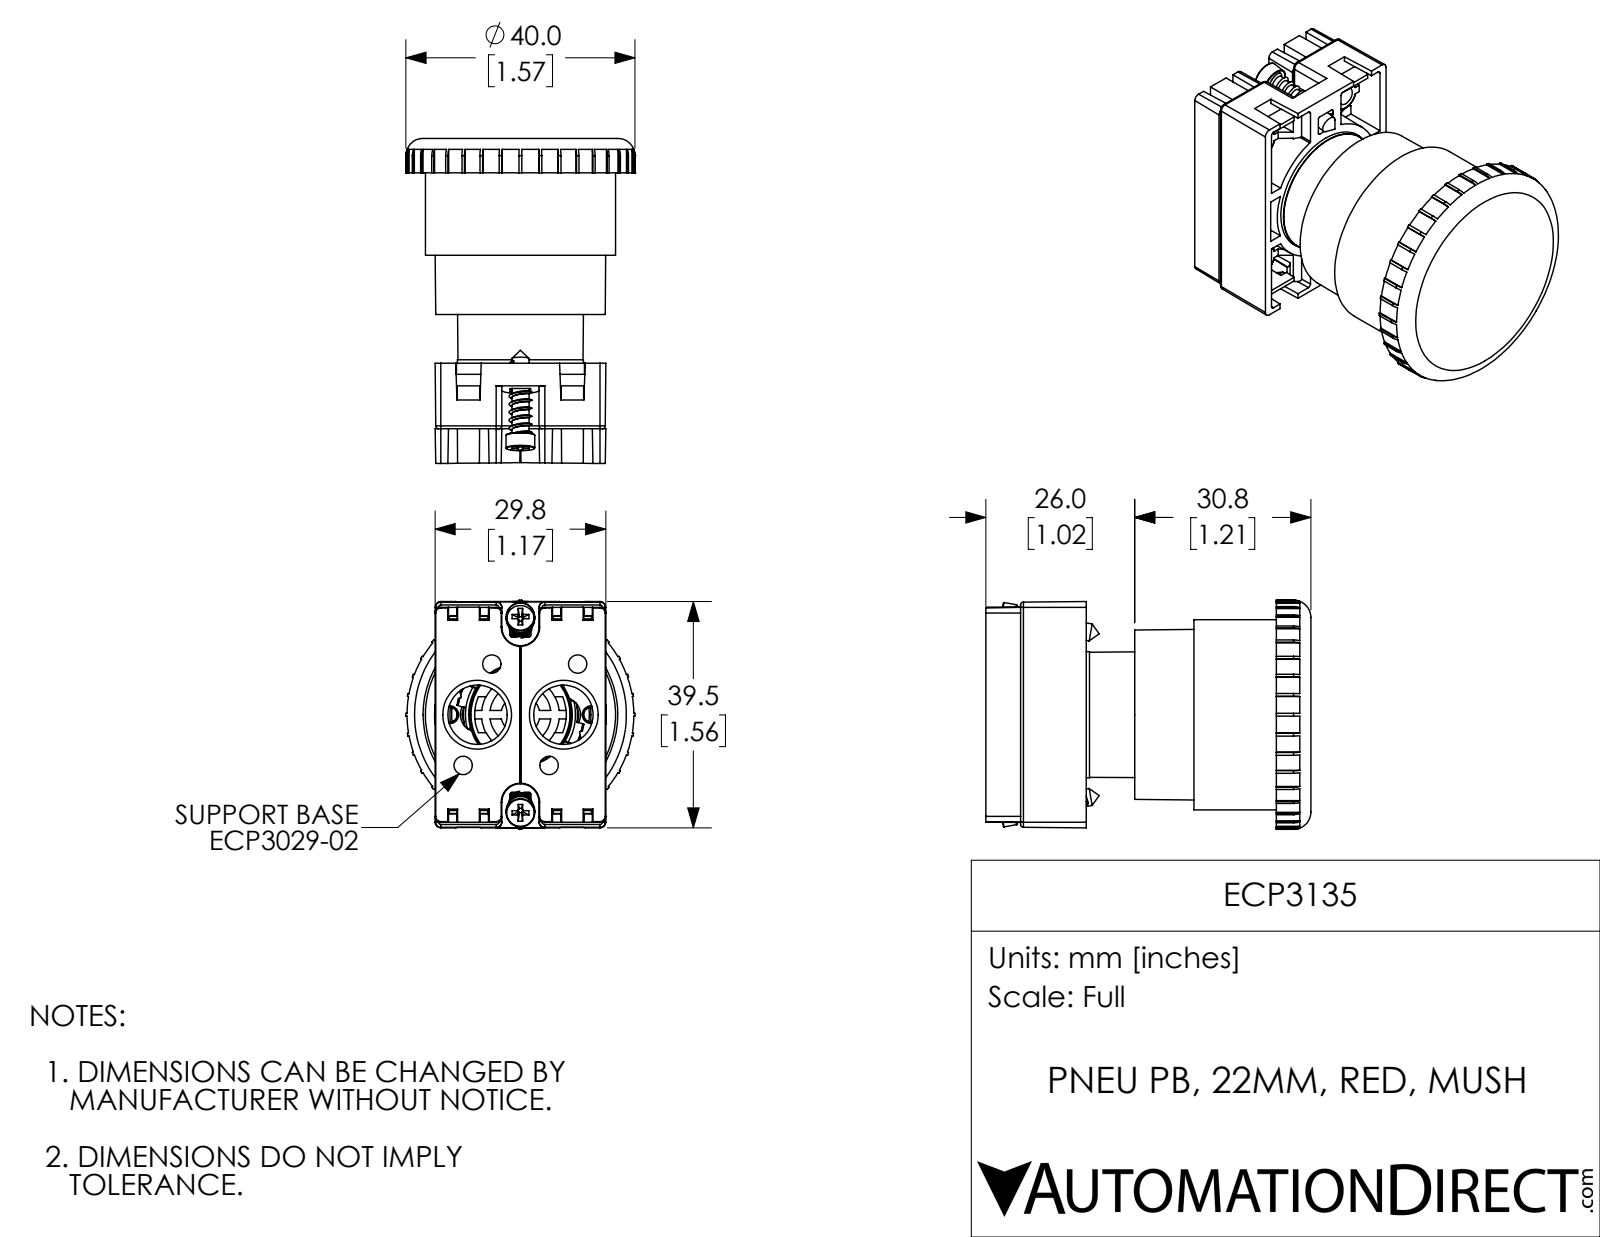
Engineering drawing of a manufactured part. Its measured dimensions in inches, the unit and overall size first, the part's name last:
Units: inches
Overall size (bounding box): 2.234 × 1.575 × 1.575
Round holes (diameter × count): ⌀0.081 ×4, ⌀0.407 ×2, ⌀0.102 ×1, ⌀0.421 ×1, ⌀0.697 ×1, ⌀0.748 ×1, ⌀0.756 ×1, ⌀1.181 ×1, ⌀1.457 ×1
Round bosses / shafts (diameter × count): ⌀0.197 ×2, ⌀0.118 ×2, ⌀1.559 ×1, ⌀1.307 ×1, ⌀0.886 ×1, ⌀0.866 ×1, ⌀0.535 ×1
Partial cylindrical surfaces — rounded edges, fillets, slot ends (radius × count): R0.02 ×18, R0.006 ×8, R0.012 ×8, R0.008 ×4, R0.039 ×4, R0.008 ×2, R0.118 ×2, R0.128 ×2
Main face-to-face distances: 1.995, 0.059, 1.936, 0.177, 0.067, 0.715, 1.544, 1.485, 0.451, 0.587
Hole centre spacings: 0.304, 0.541, 0.817, 0.295, 0.472, 0.972, 1.081, 0.591
Volume: 1.199 in³ · Surface area: 39.12 in²
Bodies: 7 solids, 993 faces (478 planar, 233 cylindrical, 282 other)
Part name (STEP PRODUCT): ECP3135
STEP written by: SolidWorks 2017 (AUTOMOTIVE_DESIGN)
